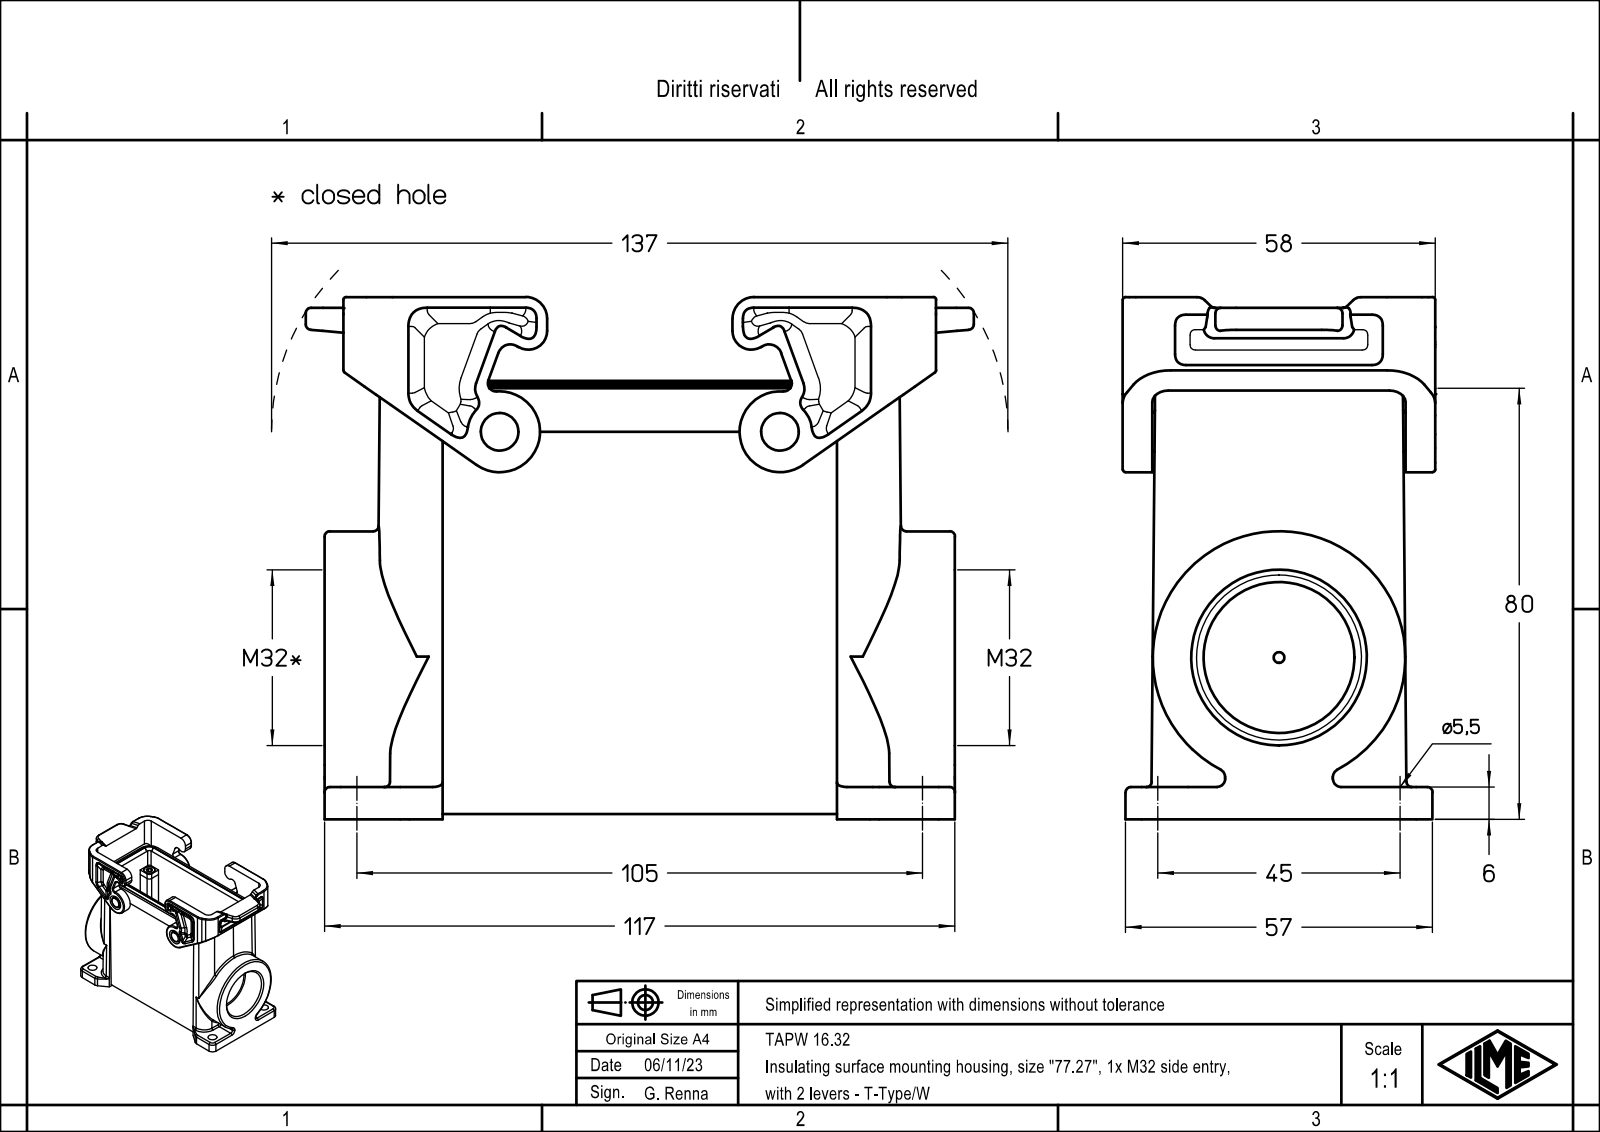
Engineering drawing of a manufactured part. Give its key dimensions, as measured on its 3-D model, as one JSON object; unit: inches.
{"part_name": "TAPW 16.32", "step_written_by": "Creo Elements/Direct Modeling 20.1B 02-Apr-2019 (C) Parametric Technology GmbH (AUTOMOTIVE_DESIGN)", "units": "inches", "bodies": {"solids": 1, "faces": 418, "planar": 208, "cylindrical": 158, "other": 52}, "overall_size": [4.882, 3.815, 2.283], "volume_in3": 12.1, "surface_area_in2": 108.1, "round_holes": [[0.217, 4], [1.102, 1], [1.205, 1]], "round_bosses_or_shafts": [[0.276, 2], [1.845, 1]], "partial_cylinders_radius": [[0.118, 20], [0.039, 16], [0.079, 16], [0.059, 10], [0.051, 8], [0.236, 8], [0.276, 8], [0.157, 6]], "face_to_face_distances": [1.386, 0.217, 0.232, 1.618, 0.256, 0.039, 0.449, 1.835, 2.067, 0.197], "hole_center_spacings": [1.772, 4.134, 4.498]}
